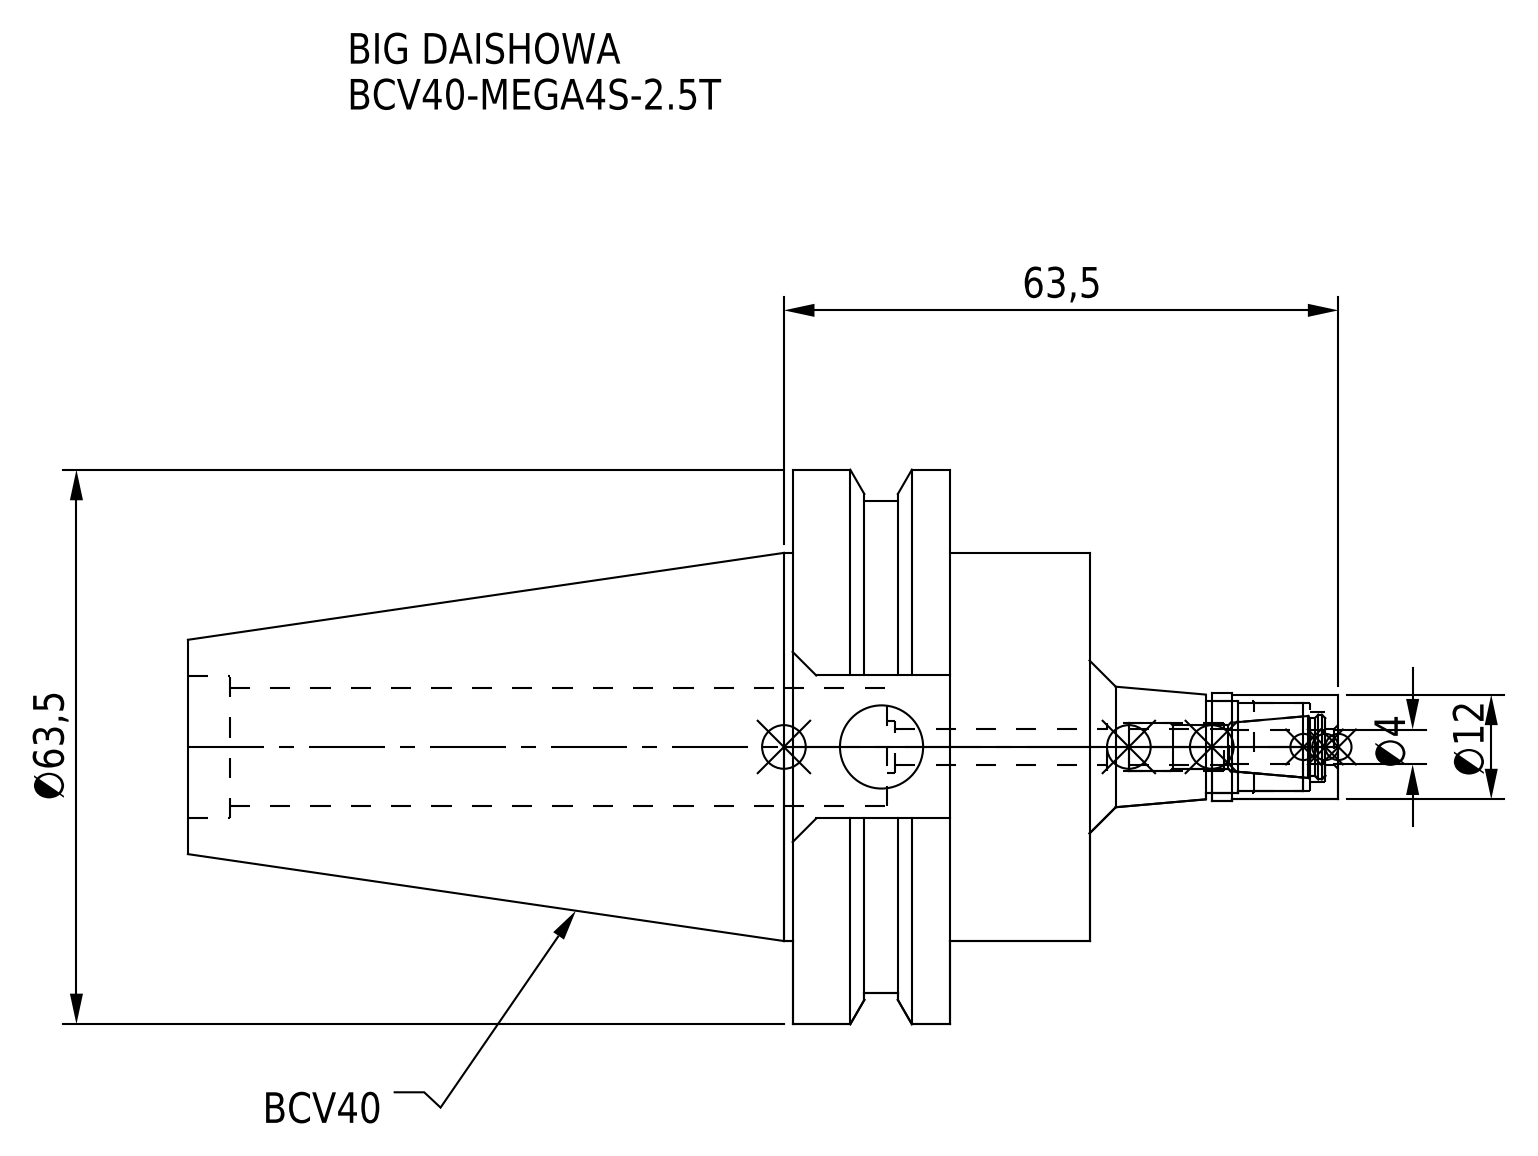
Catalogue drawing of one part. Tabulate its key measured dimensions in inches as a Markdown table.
| quantity | value |
| --- | --- |
| part name | DXF_TEMP_ASSY_ASM_4_ASM.stp; BCV40-MEGA4S-2_5T_1.stp; MGN4S_1.stp; BCV40-MEGA4S-2_5T (+3 more) |
| STEP written by | SolidWorks 2019 (CONFIG_CONTROL_DESIGN) |
| units | inches |
| bodies | 2 solids, 86 faces (32 planar, 40 cylindrical, 14 other) |
| overall size | 5.187 × 2.5 × 2.415 |
| volume | 8.069 in³ |
| surface area | 39.29 in² |
| round holes (diameter × count) | 0.161 × 1, 0.165 × 1, 0.213 × 1, 0.236 × 1, 0.315 × 1, 0.375 × 1, 0.394 × 1, 0.413 × 1, 0.535 × 1, 0.643 × 1 |
| round bosses / shafts (diameter × count) | 2.5 × 1, 2.219 × 1, 1.75 × 1, 0.484 × 1, 0.472 × 1 |
| main face-to-face distances | 0.711, 0.628, 1.339, 4.065, 3.437, 2.726, 1.872, 0.645, 0.915, 0.287 |
